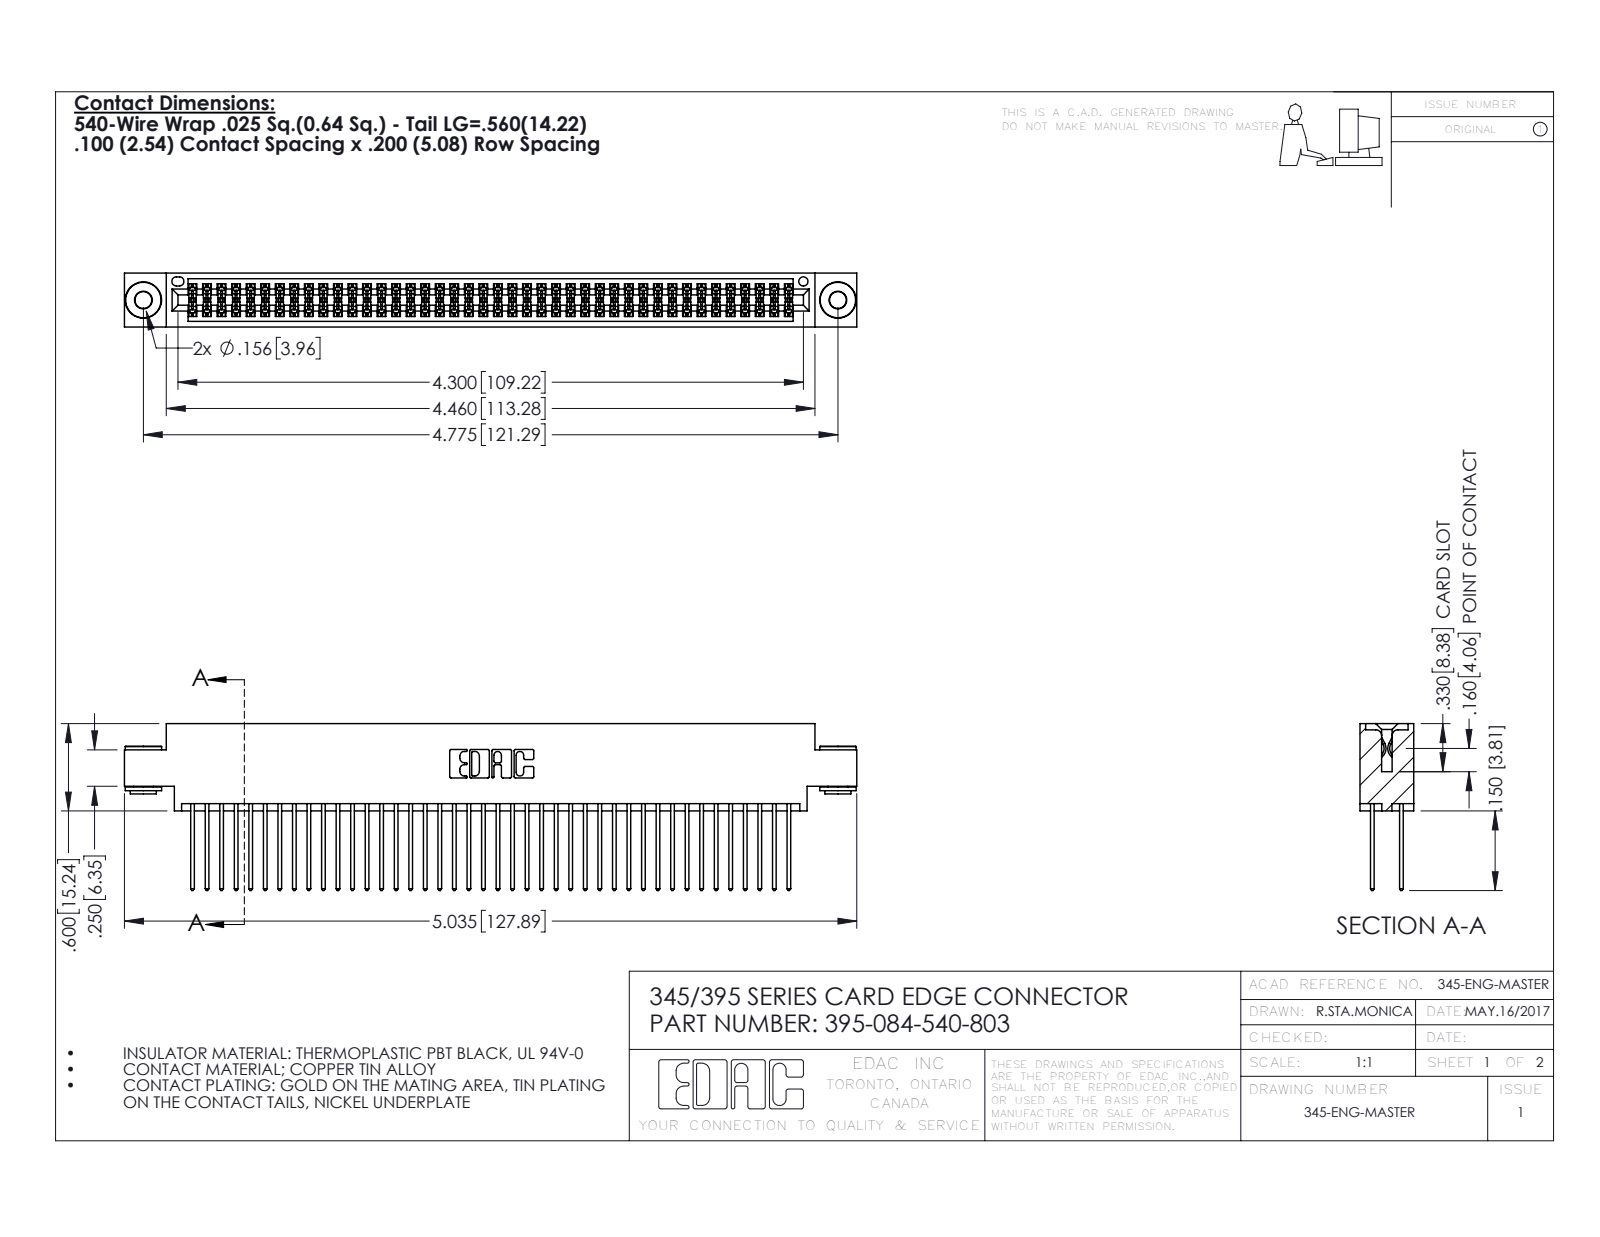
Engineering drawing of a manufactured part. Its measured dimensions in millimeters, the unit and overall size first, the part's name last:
Units: millimetres
Overall size (bounding box): 127.9 × 29.1 × 9.4
Round holes (diameter × count): ⌀2.9 ×2, ⌀4 ×2, ⌀1.6 ×1
Round bosses / shafts (diameter × count): ⌀6.4 ×2, ⌀4.6 ×2, ⌀3.5 ×2
Partial cylindrical surfaces — rounded edges, fillets, slot ends (radius × count): R0.2 ×126, R0.3 ×84, R0.3 ×22, R0.2 ×6, R0.8 ×6, R0.7 ×3, R0.4 ×2, R0.5 ×2
Main face-to-face distances: 1.8, 7.6, 5.1, 2.5, 6.9, 0.6, 9.4, 5.7, 4.4, 3.8
Hole centre spacings: 6.9, 115.3, 121.3
Volume: 12 700 mm³ · Surface area: 20 520 mm²
Bodies: 87 solids, 4368 faces (2866 planar, 1494 cylindrical, 8 other)
Part name (STEP PRODUCT): 345 Part_0.170 Offset - 0.156 Dia-TH; 345-292-001_345-293-140; 345-250-002_345-250-002-102; 395-084-540-803
STEP written by: SolidWorks 2016 (CONFIG_CONTROL_DESIGN)
